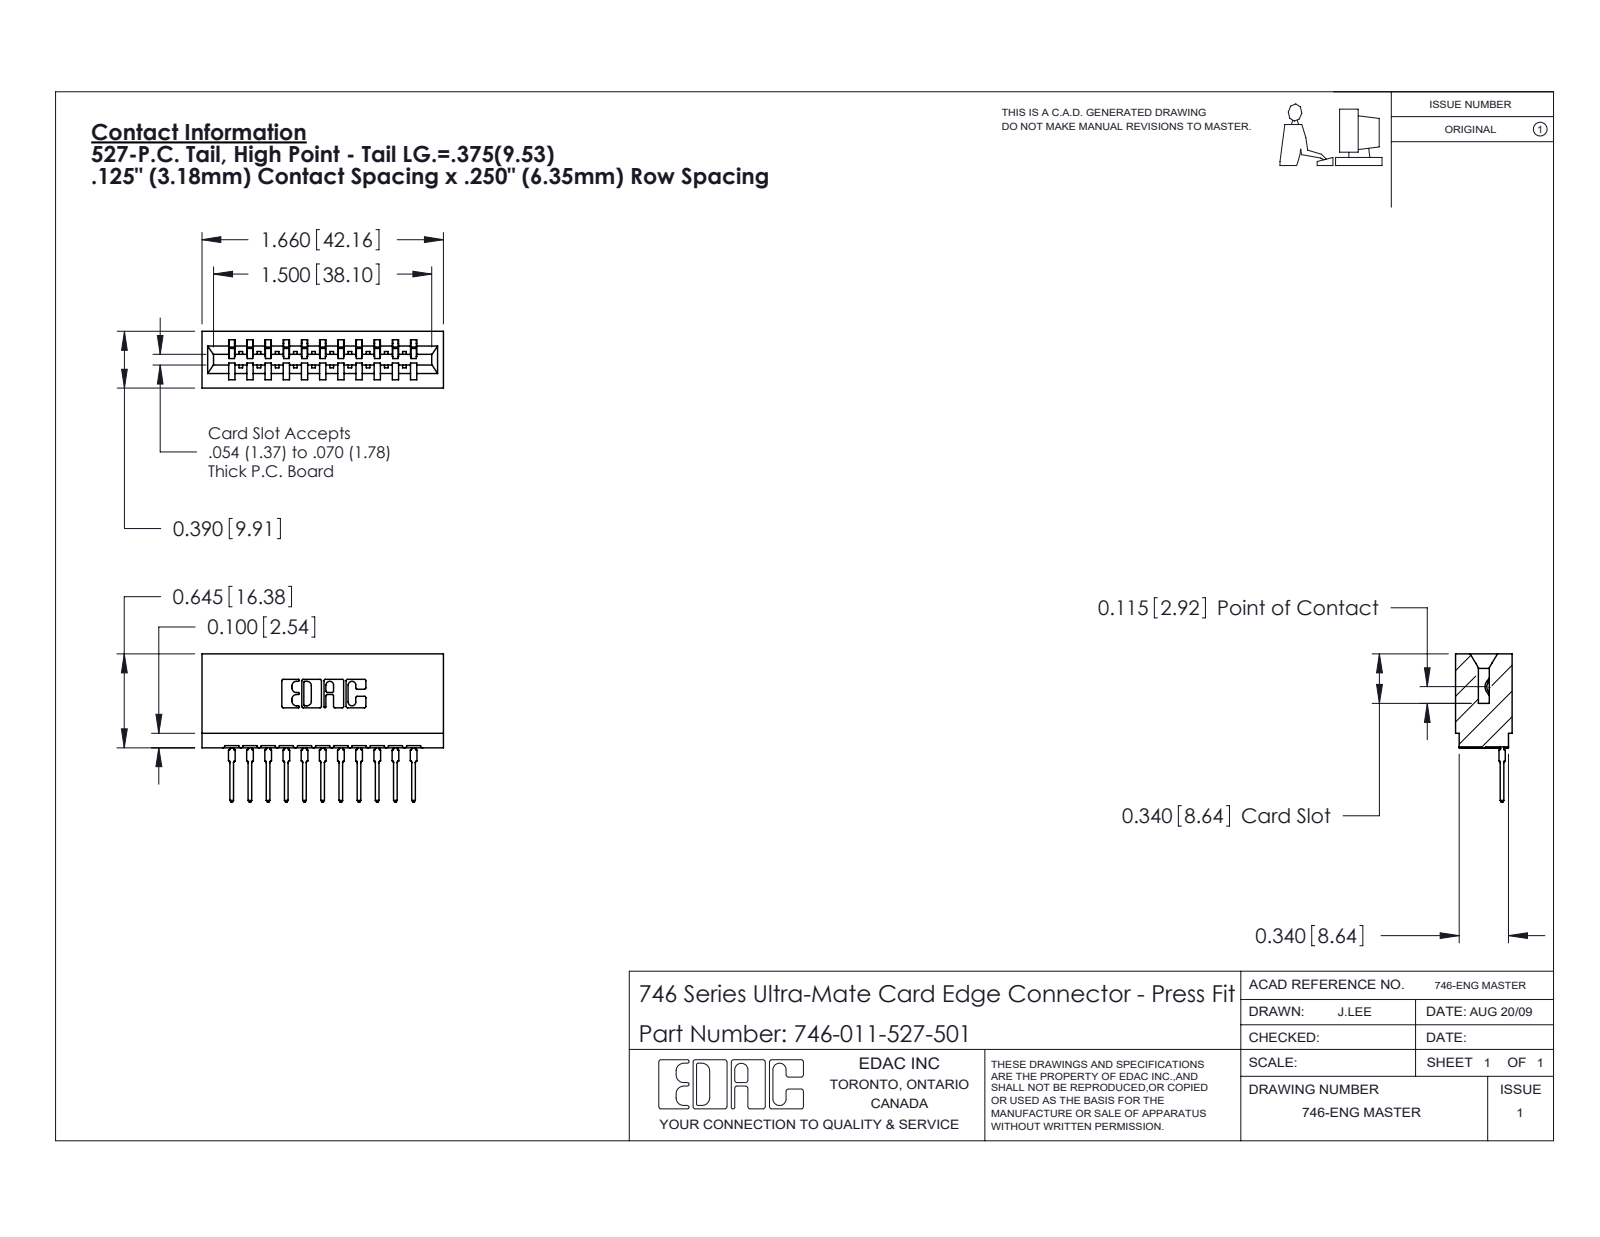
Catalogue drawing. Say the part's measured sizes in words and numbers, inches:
The part is named "746-011-527-501; 746-292-001_527; 746 Part_.340 Slot Depth - 01". Its 3-D file was written by "SolidWorks 2020 (CONFIG_CONTROL_DESIGN)". It is 12 solids with 1285 faces: 748 planar, 251 cylindrical and 286 other. Overall it measures 1.66 by 1.019 by 0.39 inches. Its volume is 0.301 cubic inches and its surface area 9.676 square inches. Partial cylindrical surfaces (rounded edges, fillets, slot ends): 22 of radius 0.01, 22 of radius 0.021, 12 of radius 0.015, 6 of radius 0.007, 6 of radius 0.031, 4 of radius 0.005, 4 of radius 0.011, 3 of radius 0.026. The main face-to-face distances are 0.25, 0.5, 0.333, 0.057, 0.125, 0.292, 0.125, 0.042, 0.542, 0.39.
